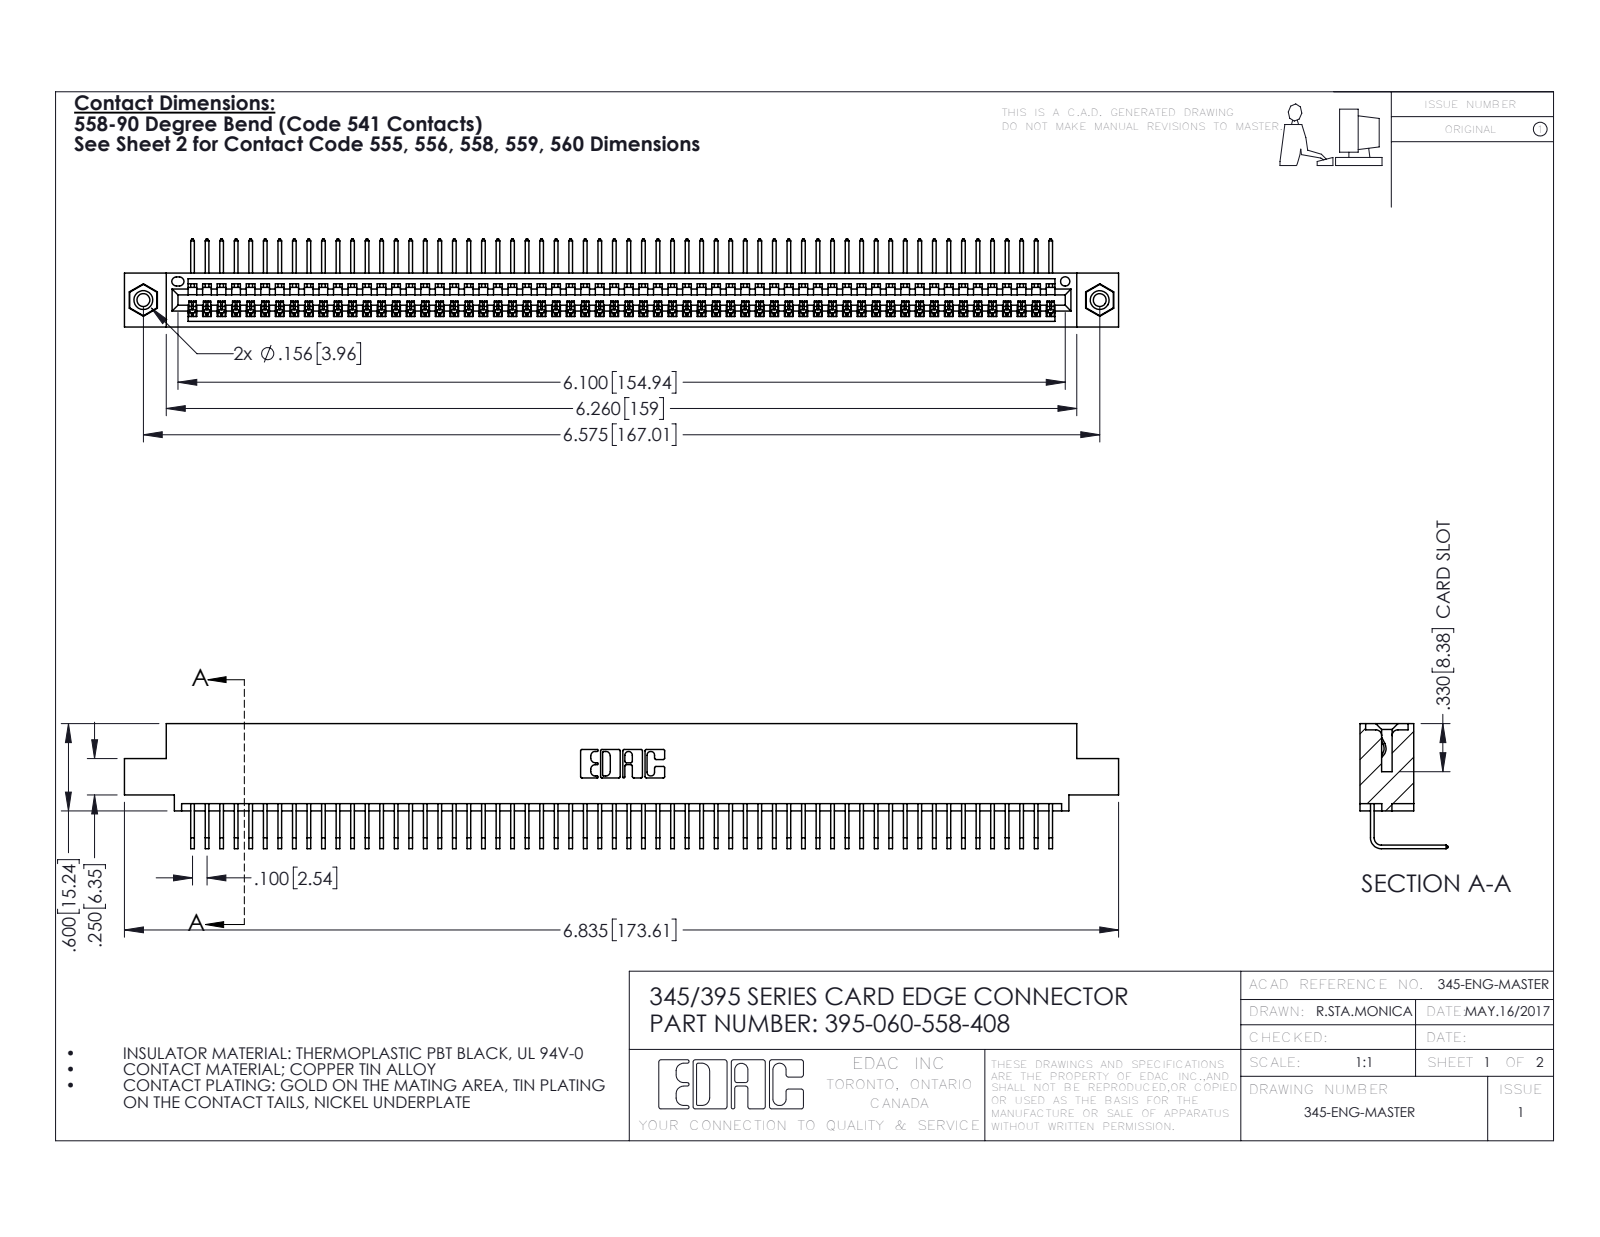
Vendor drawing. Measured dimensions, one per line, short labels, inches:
name: 345-250-001_345-250-003-102; 395-060-558-408; 345-292-001_558 Tail - 2; 345 Part_0.110 Offset - 0.156 Dia-TI
written by: SolidWorks 2016 (CONFIG_CONTROL_DESIGN)
unit: in
bodies: 63 solids, 3790 faces (2636 planar, 1138 cylindrical, 16 other)
size: 6.835 × 0.859 × 0.605
volume: 1.023 in³; area: 36.87 in²
holes: 2× ⌀0.089, 2× ⌀0.125, 2× ⌀0.156, 1× ⌀0.064
bosses: 2× ⌀0.155
rounds: 120× R0.006, 22× R0.01, 6× R0.007, 6× R0.031, 3× R0.026, 2× R0.031, 2× R0.04, 1× R0.014
face distances: 0.072, 0.298, 0.37, 0.2, 0.098, 0.272, 0.025, 0.225, 0.149, 0.072
hole spacings: 0.27, 6.339, 6.575
